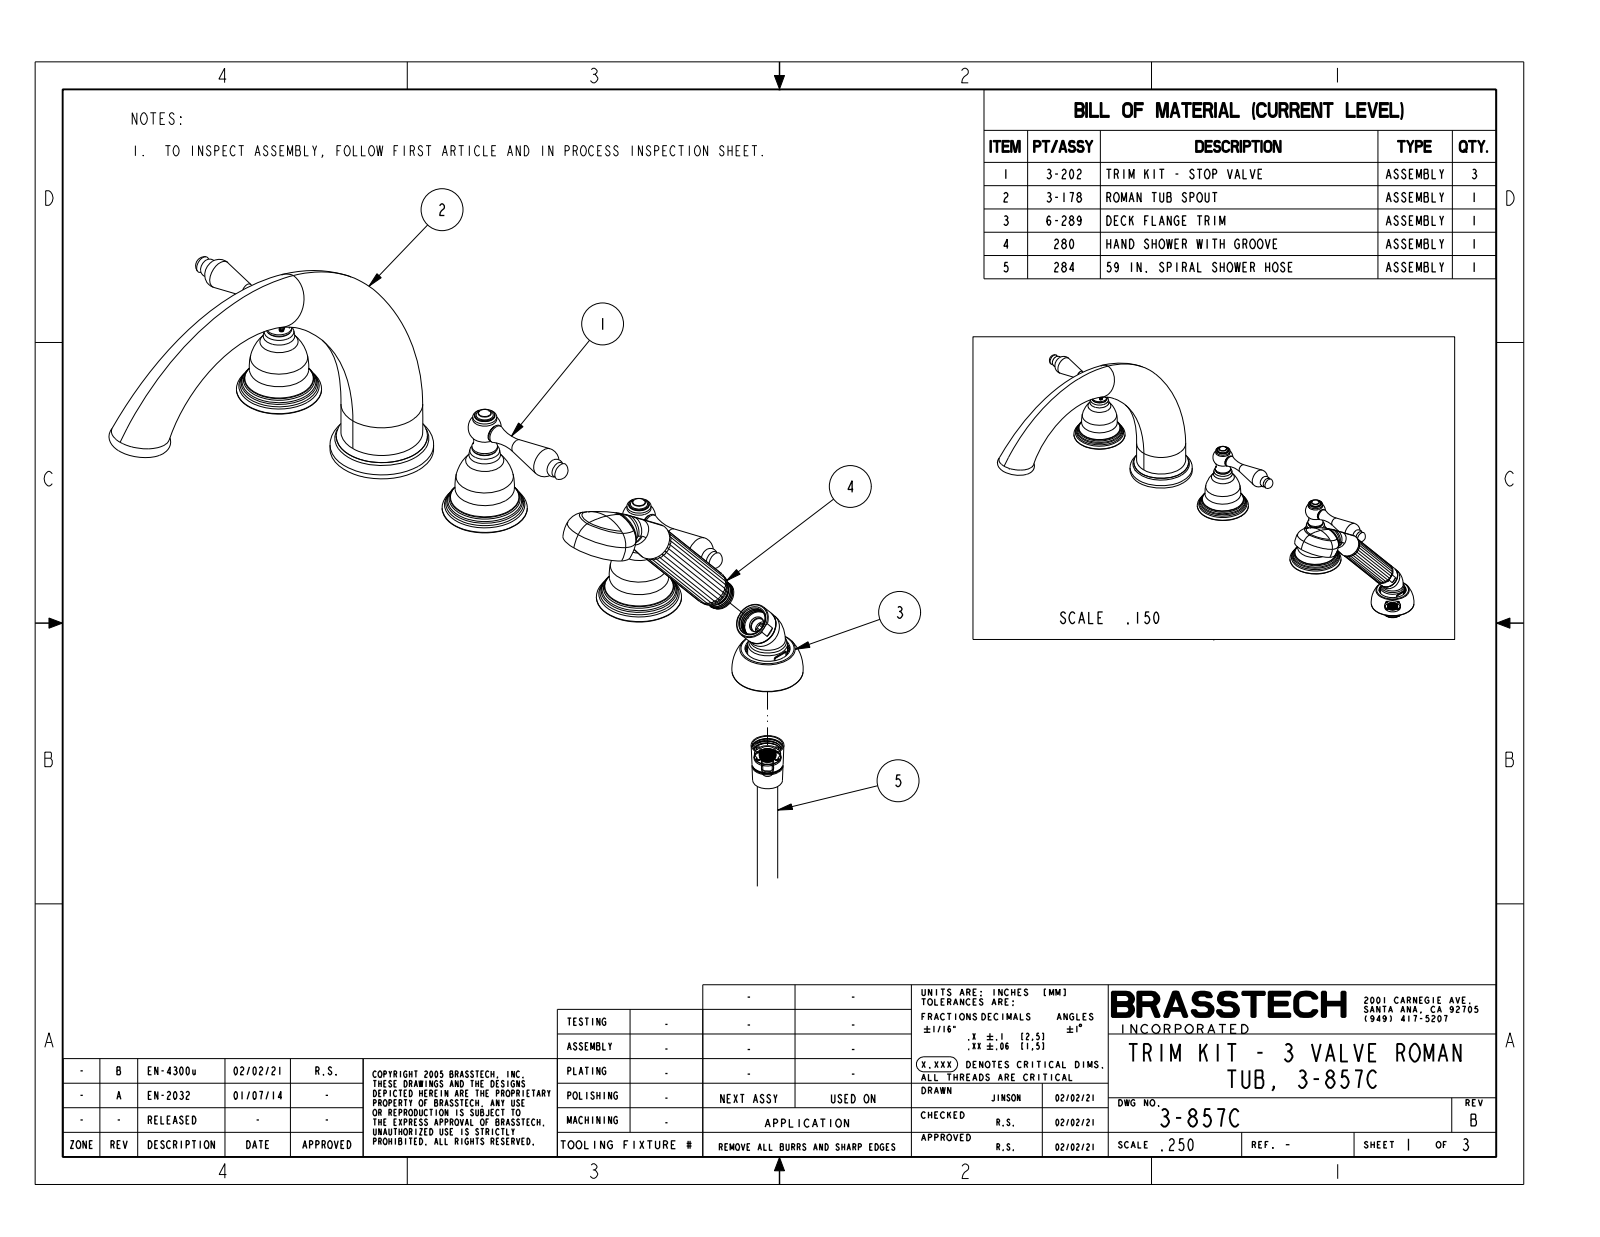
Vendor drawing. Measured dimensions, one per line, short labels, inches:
name: 3-857C
written by: CREO PARAMETRIC BY PTC INC, 2018400 (CONFIG_CONTROL_DESIGN)
unit: in
bodies: 5 solids, 637 faces (80 planar, 166 cylindrical, 391 other)
size: 23.132 × 11.68 × 7.801
volume: 60.4 in³; area: 199.1 in²
holes: 52× ⌀0.046
bosses: 3× ⌀2.34, 3× ⌀0.705, 3× ⌀0.661, 3× ⌀0.544, 3× ⌀0.4, 1× ⌀2.85, 1× ⌀2.506, 1× ⌀1.823
rounds: 6× R0.05
face distances: 2.039, 0.787, 1.252, 2.008, 1.221, 0.031, 3.209, 2.422, 1.201, 1.17
hole spacings: 0.497, 0.185, 0.185, 0.355, 0.367, 0.184, 0.187, 0.367
